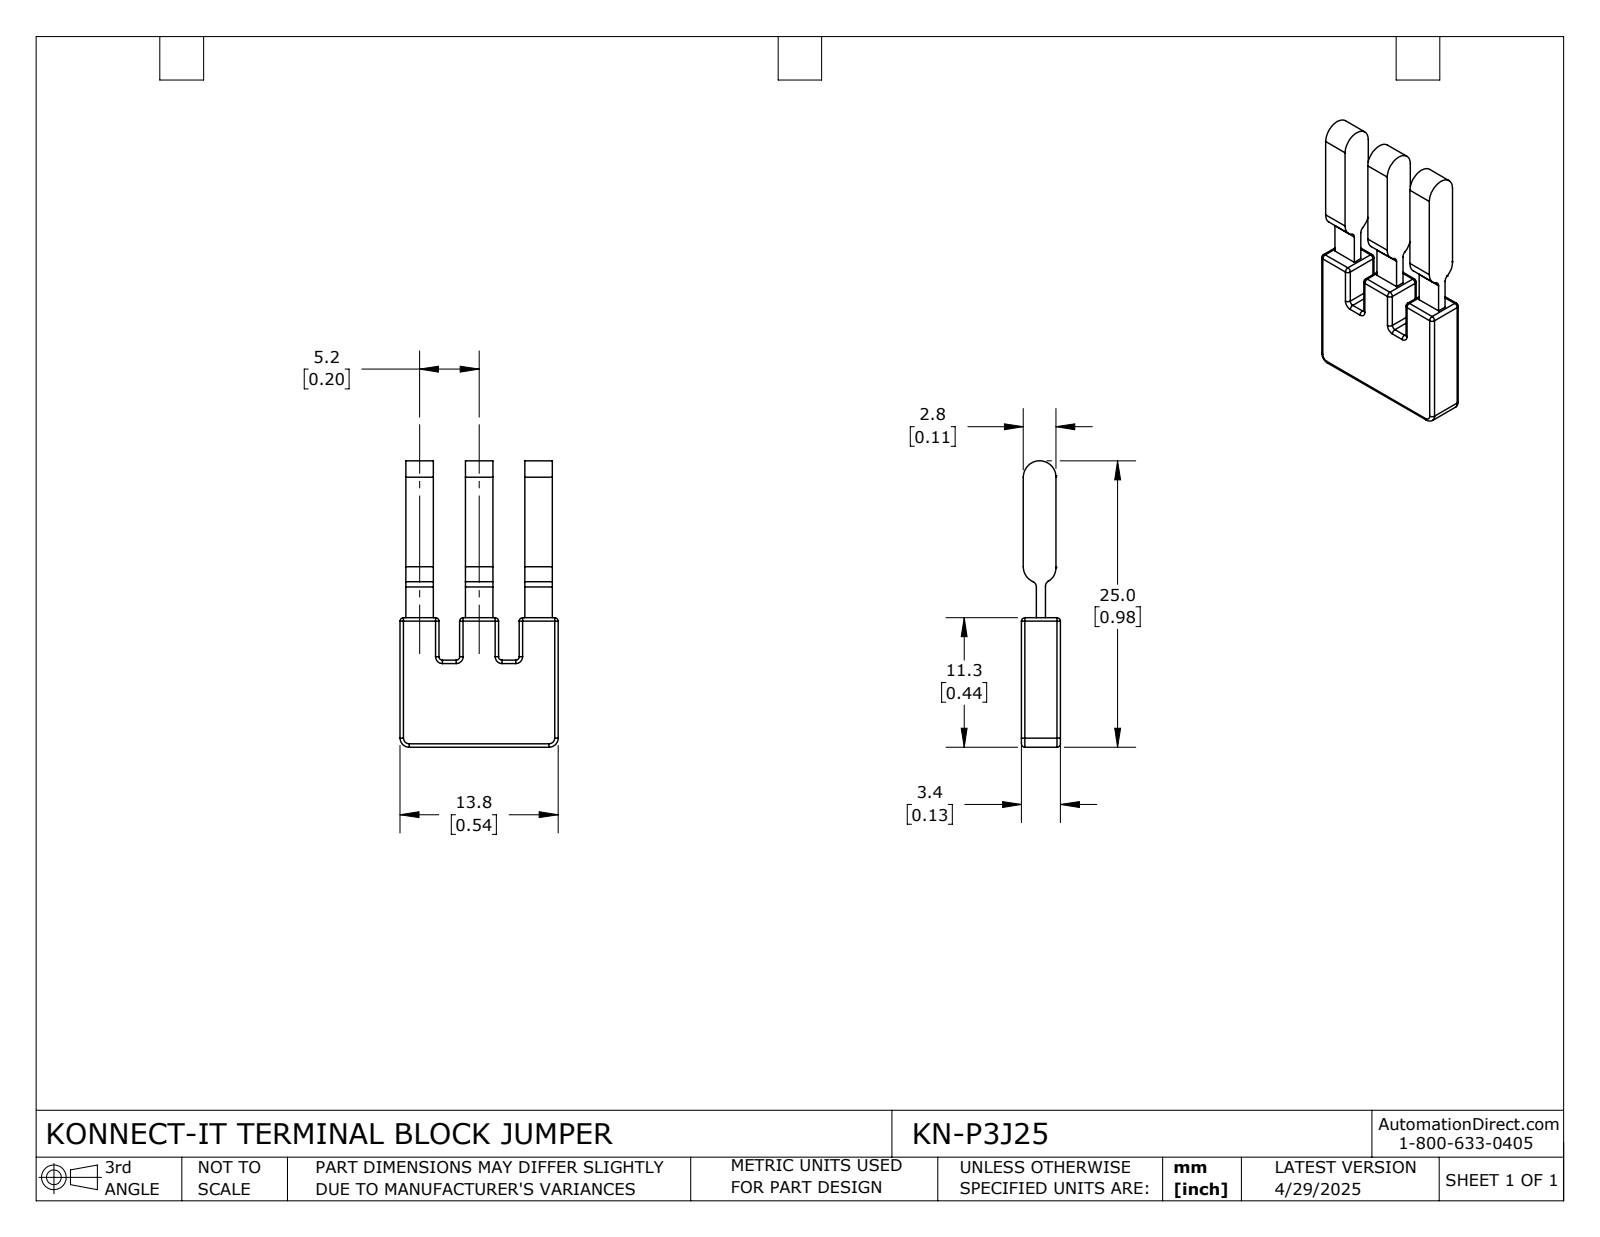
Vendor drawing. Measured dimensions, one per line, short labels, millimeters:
name: KN-P3J25
written by: SolidWorks 2024 (CONFIG_CONTROL_DESIGN)
unit: mm
bodies: 1 solid, 117 faces (36 planar, 57 cylindrical, 24 other)
size: 25 × 13.8 × 3.4
volume: 706 mm³; area: 879 mm²
rounds: 28× R0.3, 2× R0.5, 2× R0.8, 2× R1, 2× R1.43, 1× R1.3, 1× R2
face distances: 5.2, 3.4, 2.4, 0.5, 2.9, 10.4, 5.7, 8.1, 7.6, 2.8
